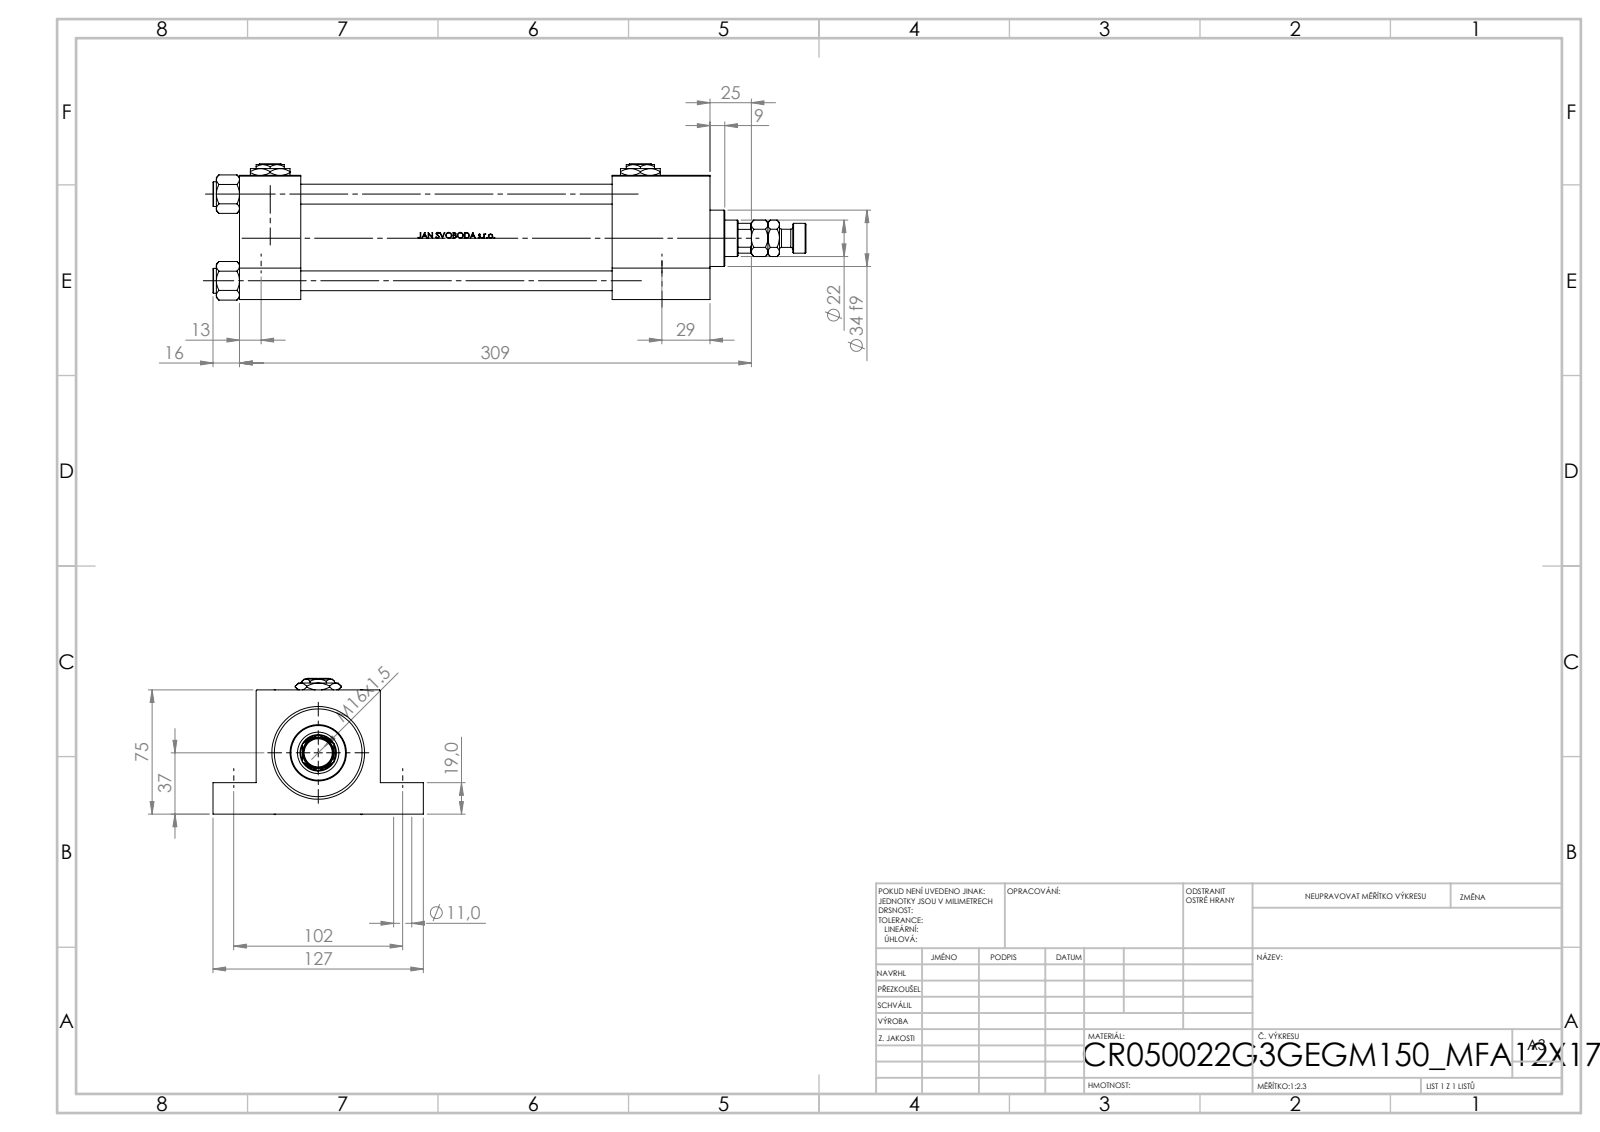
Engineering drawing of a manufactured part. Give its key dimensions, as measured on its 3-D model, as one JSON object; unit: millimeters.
{"part_name": "Zatka_pro_OIL_PORT; MFA; V215CR_G_TYCINKA; V215_VC_A (+3 more)", "step_written_by": "SolidWorks 2019 (CONFIG_CONTROL_DESIGN)", "units": "millimeters", "bodies": {"solids": 18, "faces": 1304, "planar": 512, "cylindrical": 140, "other": 652}, "overall_size": [358, 127, 82.27], "volume_mm3": 1002000, "surface_area_mm2": 260754, "round_holes": [[12, 4], [14, 4], [7, 2], [20.96, 2], [30, 2], [10.5, 1], [22, 1], [25, 1], [41, 1], [50, 1], [53, 1]], "round_bosses_or_shafts": [[15, 4], [56, 1], [34, 1], [18, 1], [11, 1]], "partial_cylinders_radius": [[10.5, 1]], "face_to_face_distances": [75, 37, 284, 247, 19, 56, 225, 188, 59, 101], "hole_center_spacings": [36.98, 52.3, 51.3, 52.63, 73.96, 102, 234.61, 241.94]}
